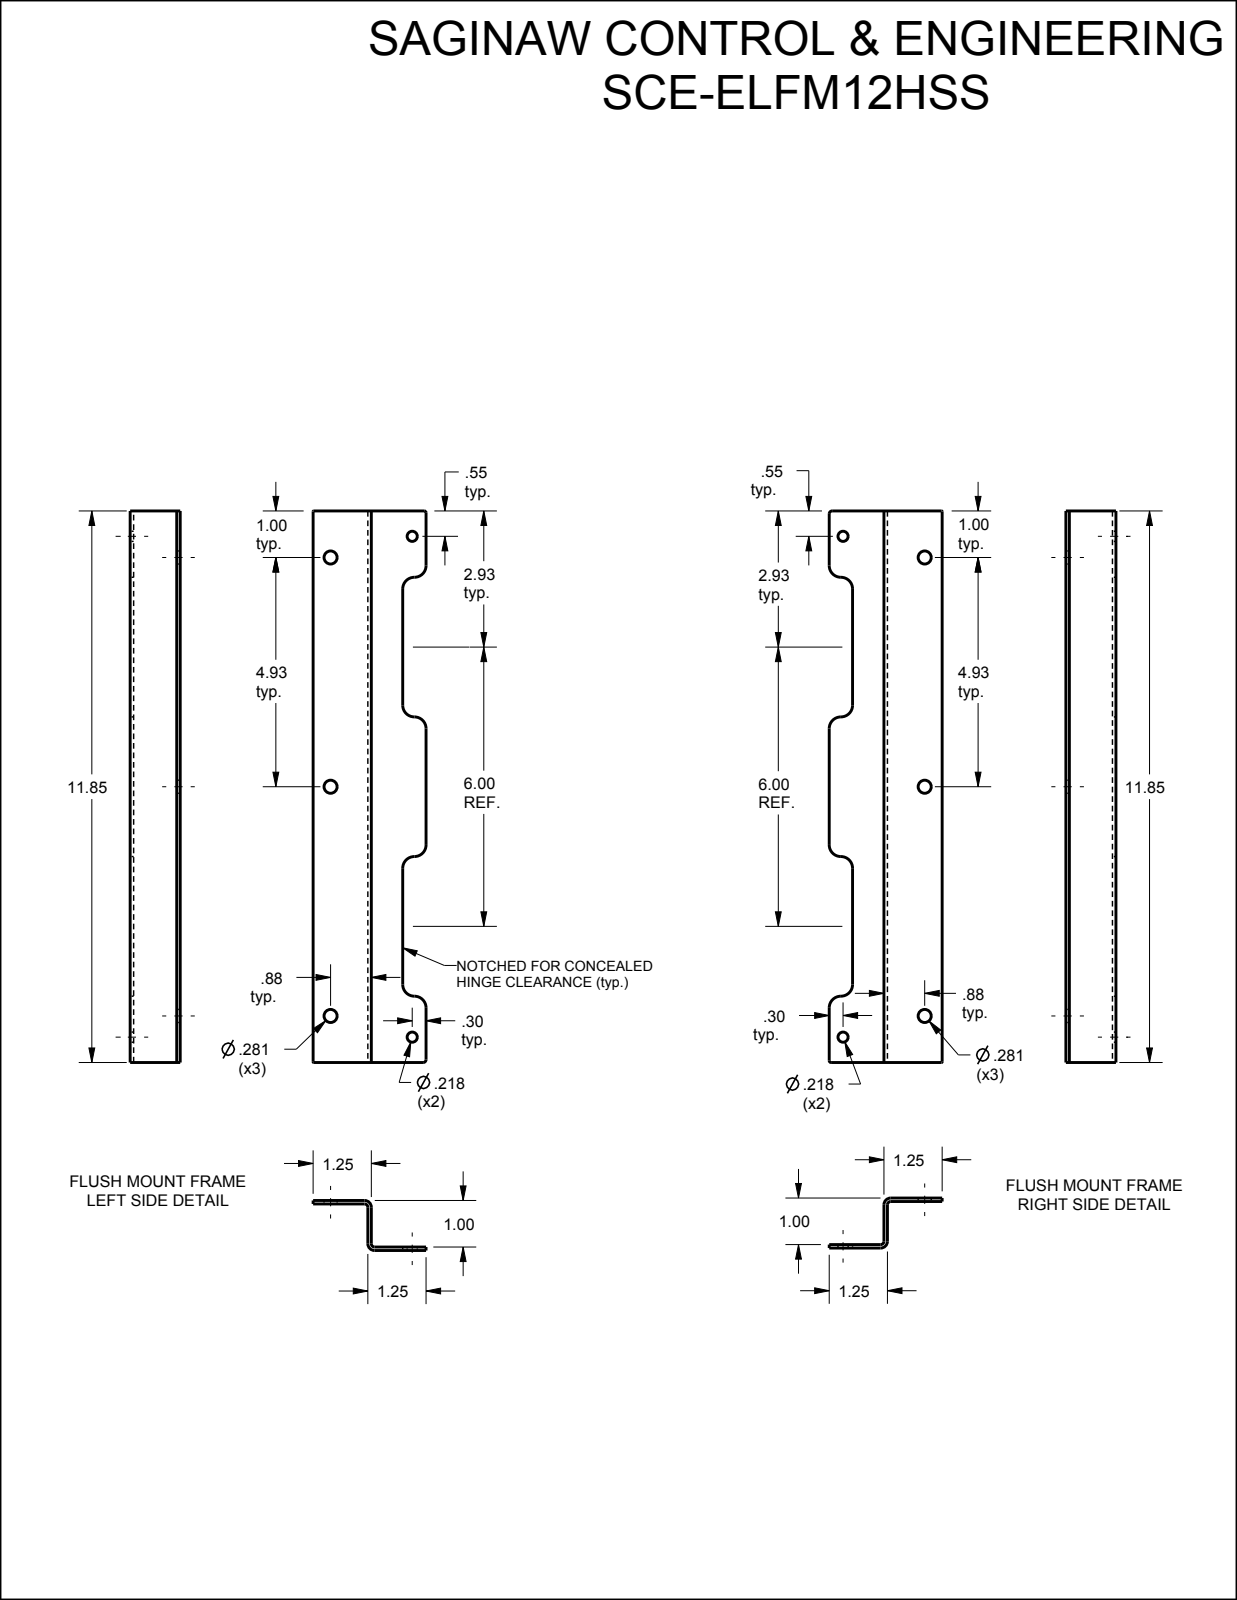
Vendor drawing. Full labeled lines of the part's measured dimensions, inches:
Part name (STEP PRODUCT): SCE-ELFM12H
STEP written by: SolidWorks 2019 (CONFIG_CONTROL_DESIGN)
Units: inches
Bodies: 2 solids, 78 faces (36 planar, 42 cylindrical, 0 other)
Overall size (bounding box): 15 × 11.85 × 1.073
Volume: 5.463 in³ · Surface area: 151 in²
Round holes (diameter × count): ⌀0.281 ×6, ⌀0.218 ×4
Partial cylindrical surfaces — rounded edges, fillets, slot ends (radius × count): R0.25 ×16, R0.015 ×4, R0.051 ×4, R0.126 ×4, R0.04 ×2, R0.062 ×2
Main face-to-face distances: 0.075, 0.075, 0.998, 1.073, 0.923, 0.998, 12.575, 12.65, 12.5, 12.575
Hole centre spacings: 1.813, 4.925, 5.659, 10.453, 12.503, 13.604, 15.077, 16.196
